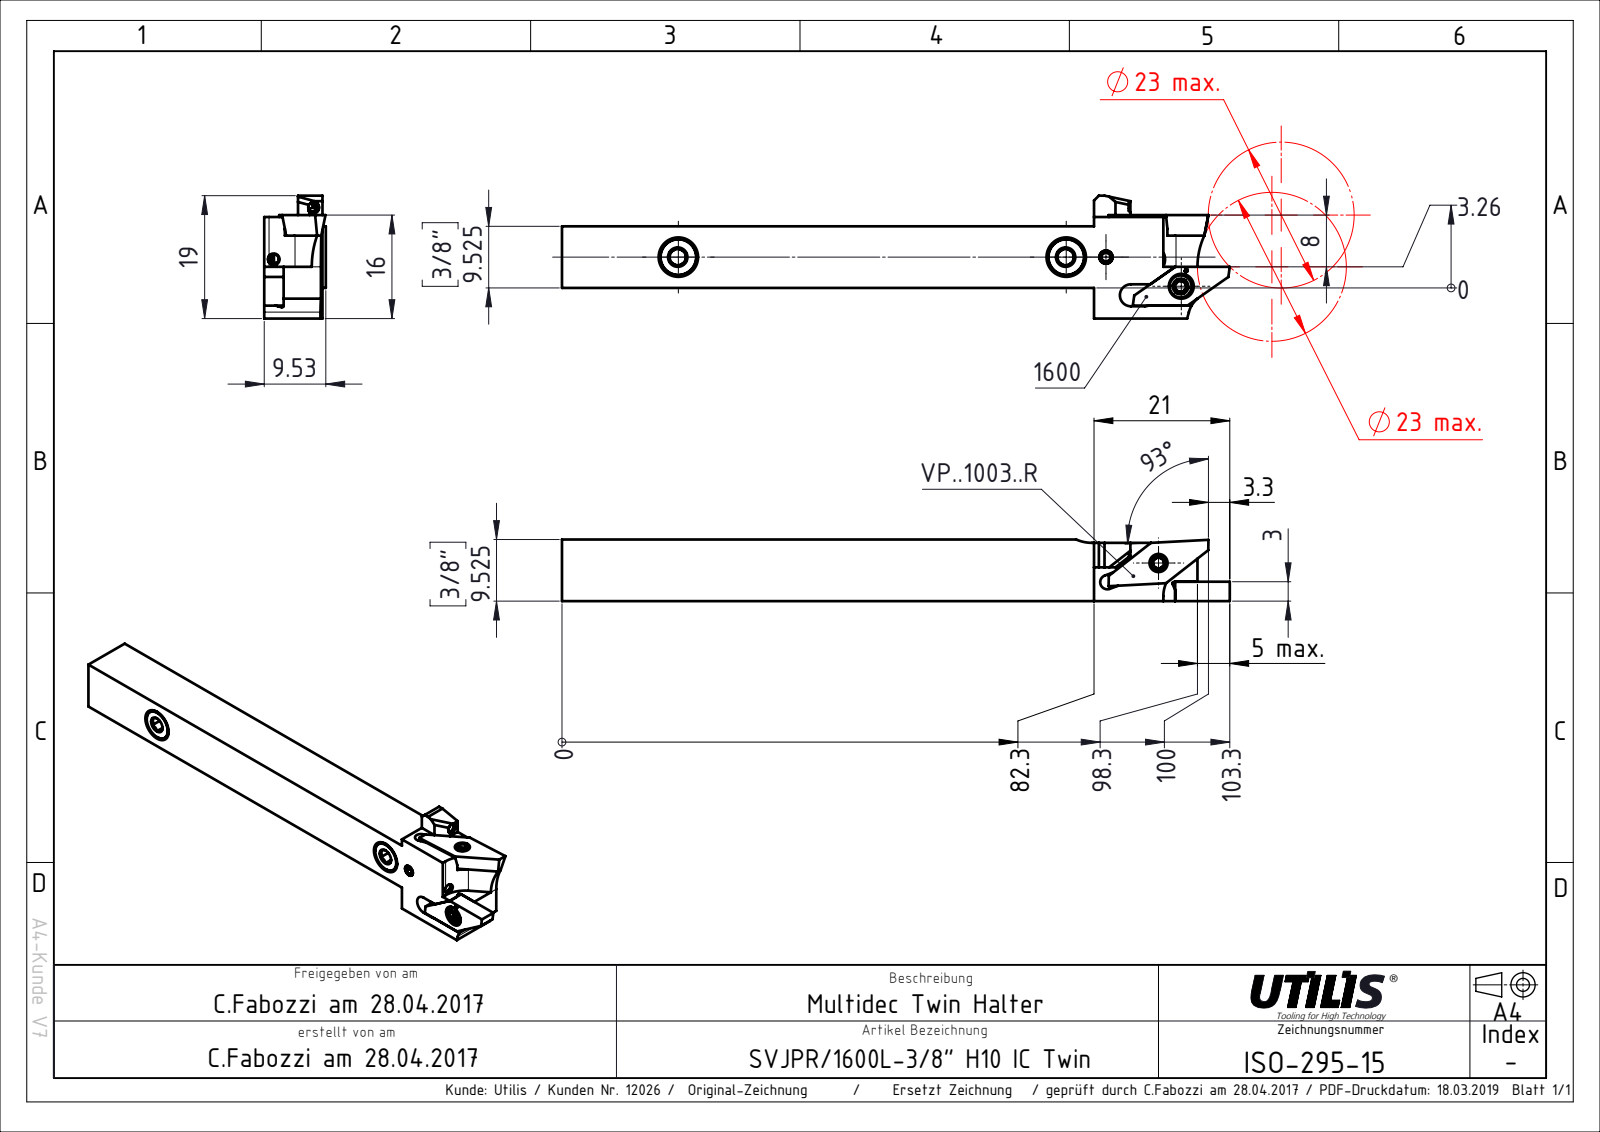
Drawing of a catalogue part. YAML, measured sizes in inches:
part_name: "ISO-295-15"
step_written_by: "SolidWorks 2016 (AUTOMOTIVE_DESIGN)"
units: inches
bodies: {solids: 1, faces: 81, planar: 67, cylindrical: 12, other: 2}
overall_size: [4.067, 0.748, 0.375]
volume: 0.586
surface_area: 6.935
partial_cylinders:
  - {radius: 0.01, count: 2}
  - {radius: 0.24, count: 2}
  - {radius: 0.02, count: 1}
  - {radius: 0.043, count: 1}
  - {radius: 0.061, count: 1}
  - {radius: 0.067, count: 1}
  - {radius: 0.161, count: 1}
  - {radius: 0.201, count: 1}
face_to_face_distances: [0.375, 0.187, 0.561, 0.63, 0.315, 3.24, 0.443, 0.069, 0.357, 0.018]
